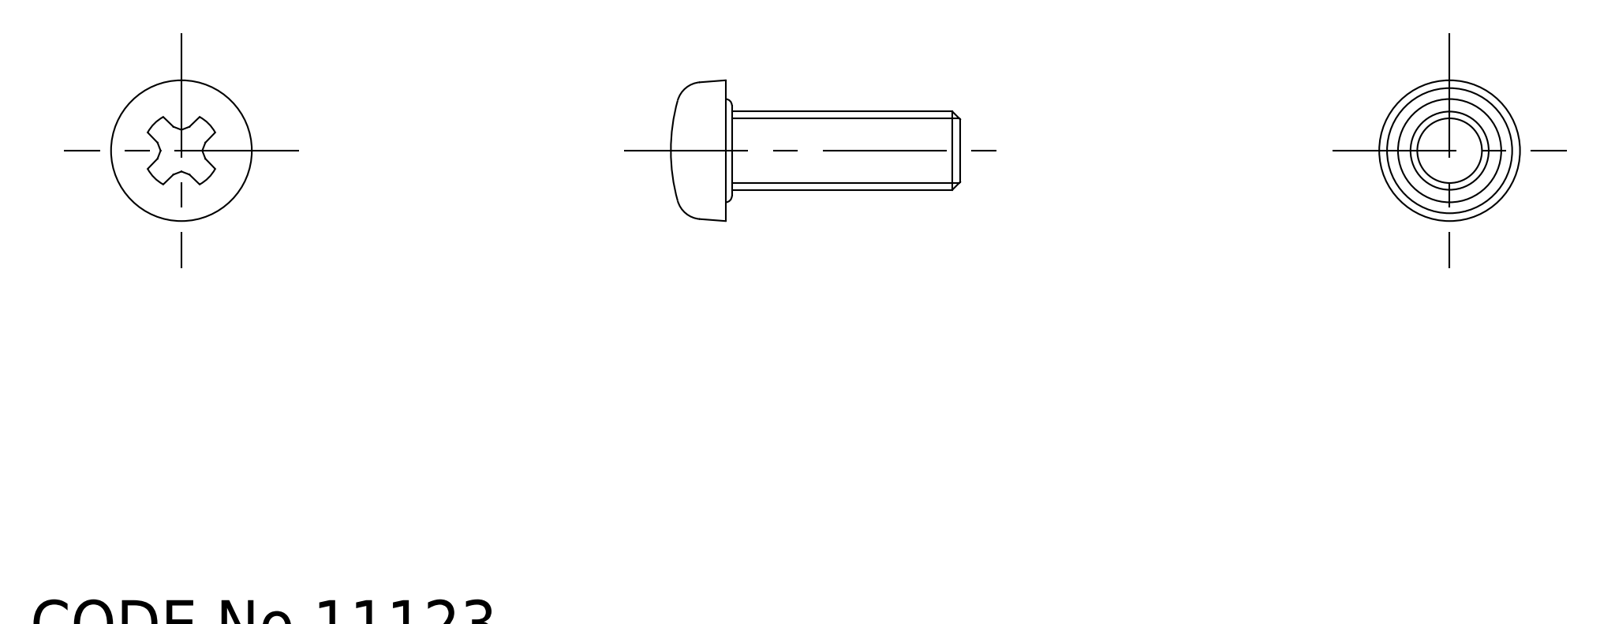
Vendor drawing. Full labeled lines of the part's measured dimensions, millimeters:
Part name (STEP PRODUCT): screw; TL_416_M5_15
STEP written by: SolidWorks 2015 (AUTOMOTIVE_DESIGN)
Units: millimetres
Bodies: 2 solids, 40 faces (20 planar, 8 cylindrical, 12 other)
Overall size (bounding box): 18.43 × 9 × 9
Volume: 461 mm³ · Surface area: 498 mm²
Round holes (diameter × count): ⌀8 ×1
Round bosses / shafts (diameter × count): ⌀5 ×1
Partial cylindrical surfaces — rounded edges, fillets, slot ends (radius × count): R2.45 ×1
Main face-to-face distances: 2.5, 0.4, 15.4, 15, 2.1, 17.5, 1.5
